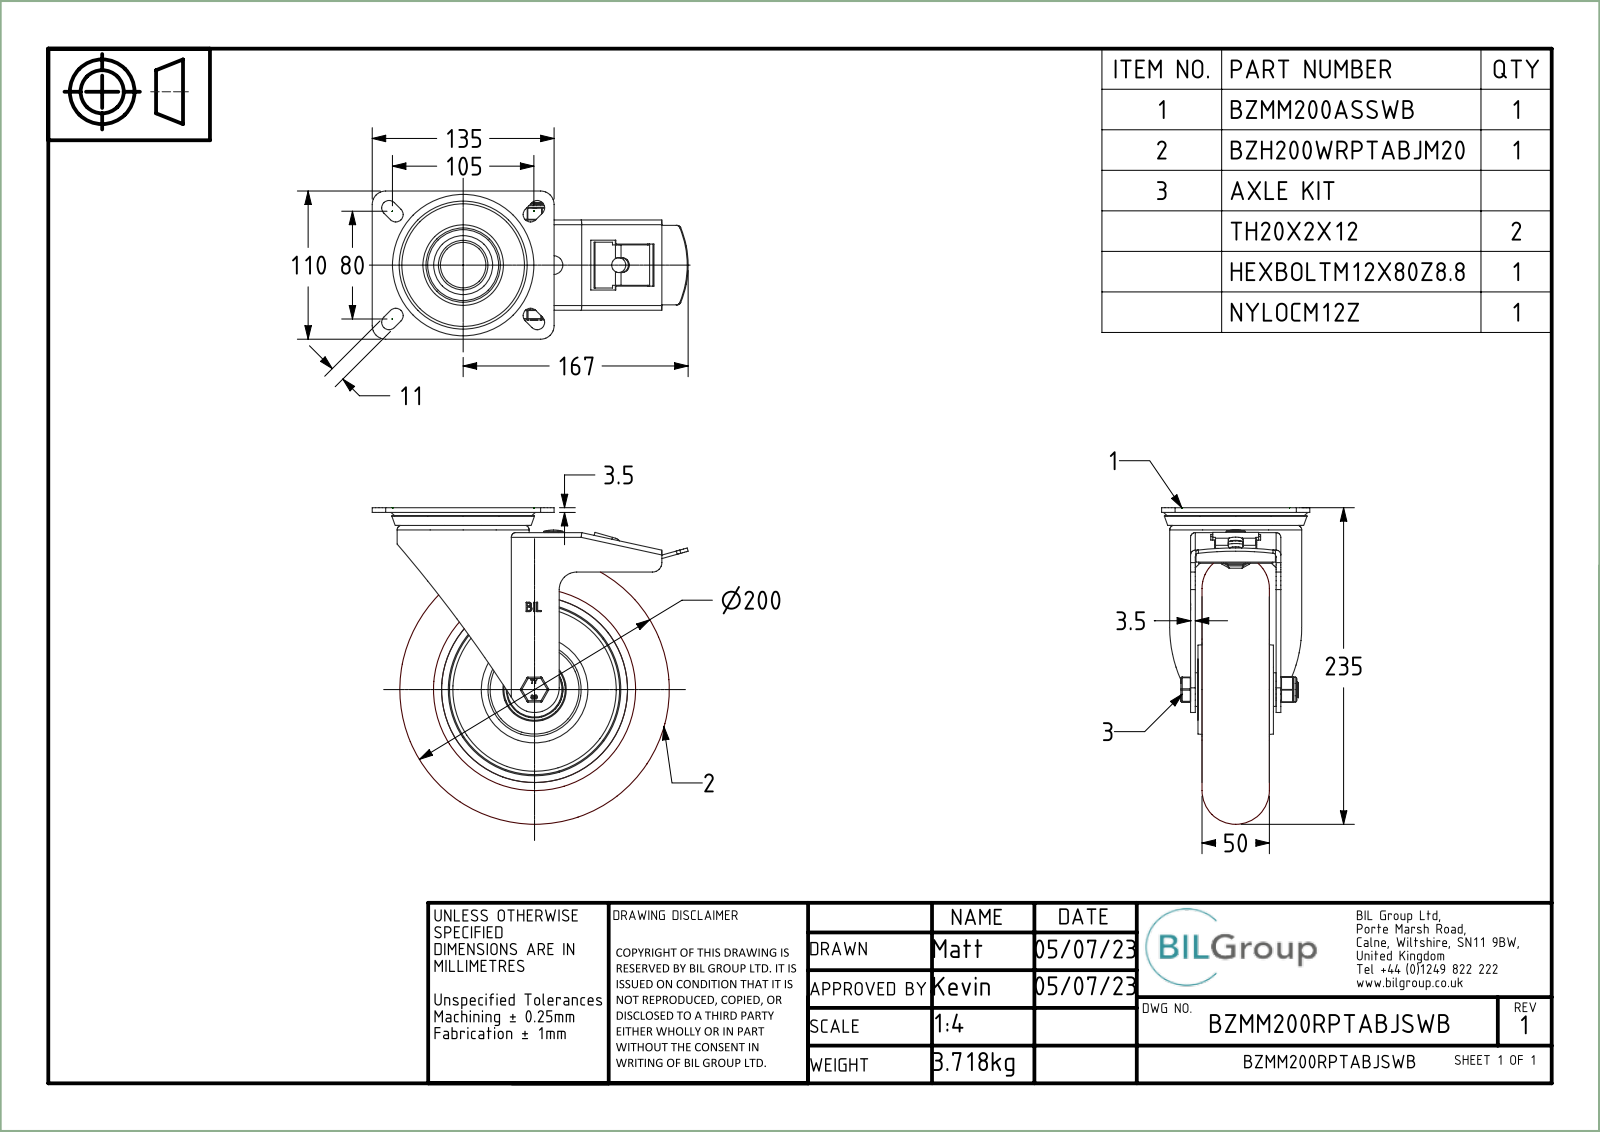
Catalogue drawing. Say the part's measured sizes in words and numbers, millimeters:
The part is named "ZINC PLATED, PRESSED STEEL TOP PLATE; ZINC PLATED, PRESSED STEEL TOP PLATE Geometry; BALL BEARINGS; BZMM200ASSWB (+7 more)". Its 3-D file was written by "Spatial InterOp 3D (CONFIG_CONTROL_DESIGN)". It is 82 solids with 1627 faces: 541 planar, 459 cylindrical and 627 other. Overall it measures 235 by 234.5 by 110 millimeters. Its volume is 1 289 000 cubic millimeters and its surface area 376 096 square millimeters. Round holes: 12 of diameter 9, 1 of diameter 8, 1 of diameter 11, 1 of diameter 12, 1 of diameter 12.2, 1 of diameter 14, 1 of diameter 20, 1 of diameter 28.5, 1 of diameter 30.8, 1 of diameter 33.75, 1 of diameter 40.3, 1 of diameter 40.5. Round bosses or shafts: 12 of diameter 9, 1 of diameter 98, 1 of diameter 78, 1 of diameter 50, 1 of diameter 40.8, 1 of diameter 39.75, 1 of diameter 31.3, 1 of diameter 27. Partial cylindrical surfaces (rounded edges, fillets, slot ends): 18 of radius 0.5, 12 of radius 1, 10 of radius 5.5, 7 of radius 1.75, 6 of radius 0.25, 6 of radius 2.5, 4 of radius 3.5, 4 of radius 10. The main face-to-face distances are 3.5, 27, 36.5, 9.5, 13, 6, 18.5, 5, 5.5, 30.5. The hole center spacings are 76.5, 39.6, 108.19, 147.79, 132.5, 132.51, 153, 153.01.
